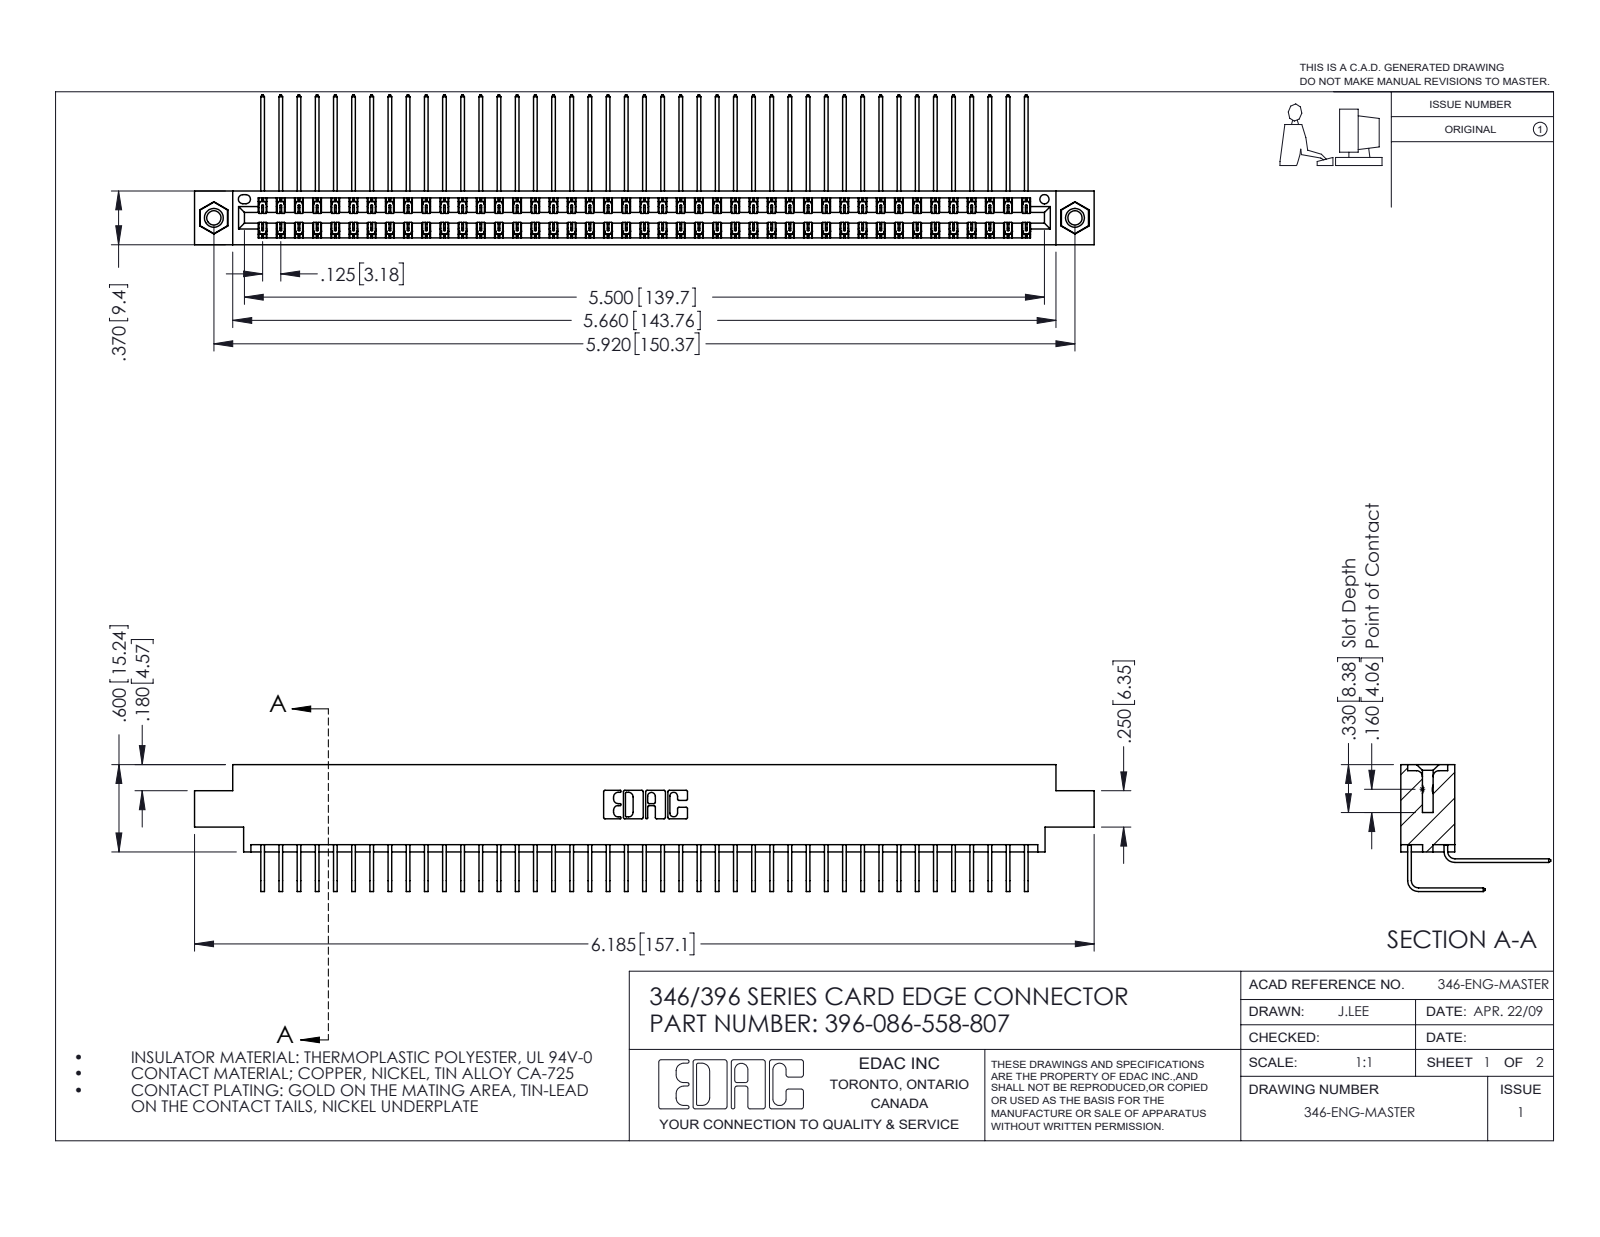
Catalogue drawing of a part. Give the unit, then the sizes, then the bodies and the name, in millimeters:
Units: millimetres
Overall size (bounding box): 157.1 × 26.2 × 22.2
Round holes (diameter × count): ⌀2.5 ×2, ⌀3.2 ×2, ⌀4 ×2, ⌀1.6 ×1
Round bosses / shafts (diameter × count): ⌀3.9 ×2
Partial cylindrical surfaces — rounded edges, fillets, slot ends (radius × count): R0.2 ×129, R0.3 ×22, R0.2 ×6, R0.8 ×6, R0.7 ×3, R0.4 ×2, R0.6 ×2, R0.6 ×2
Main face-to-face distances: 8.2, 1.2, 0.6, 9.4, 6.4, 7.6, 1.8, 7, 5.6, 3.8
Hole centre spacings: 6.2, 145.1, 150.4
Volume: 15 600 mm³ · Surface area: 24 130 mm²
Bodies: 89 solids, 4830 faces (3294 planar, 1520 cylindrical, 16 other)
Part name (STEP PRODUCT): 346 Part_0.170 Offset - 0.156 Dia-TI; 345-292-001_558 559 Tail - 1; 345-250-001_345-250-005-103; 345-292-001_558 Tail - 2 (+1 more)
STEP written by: SolidWorks 2016 (CONFIG_CONTROL_DESIGN)
